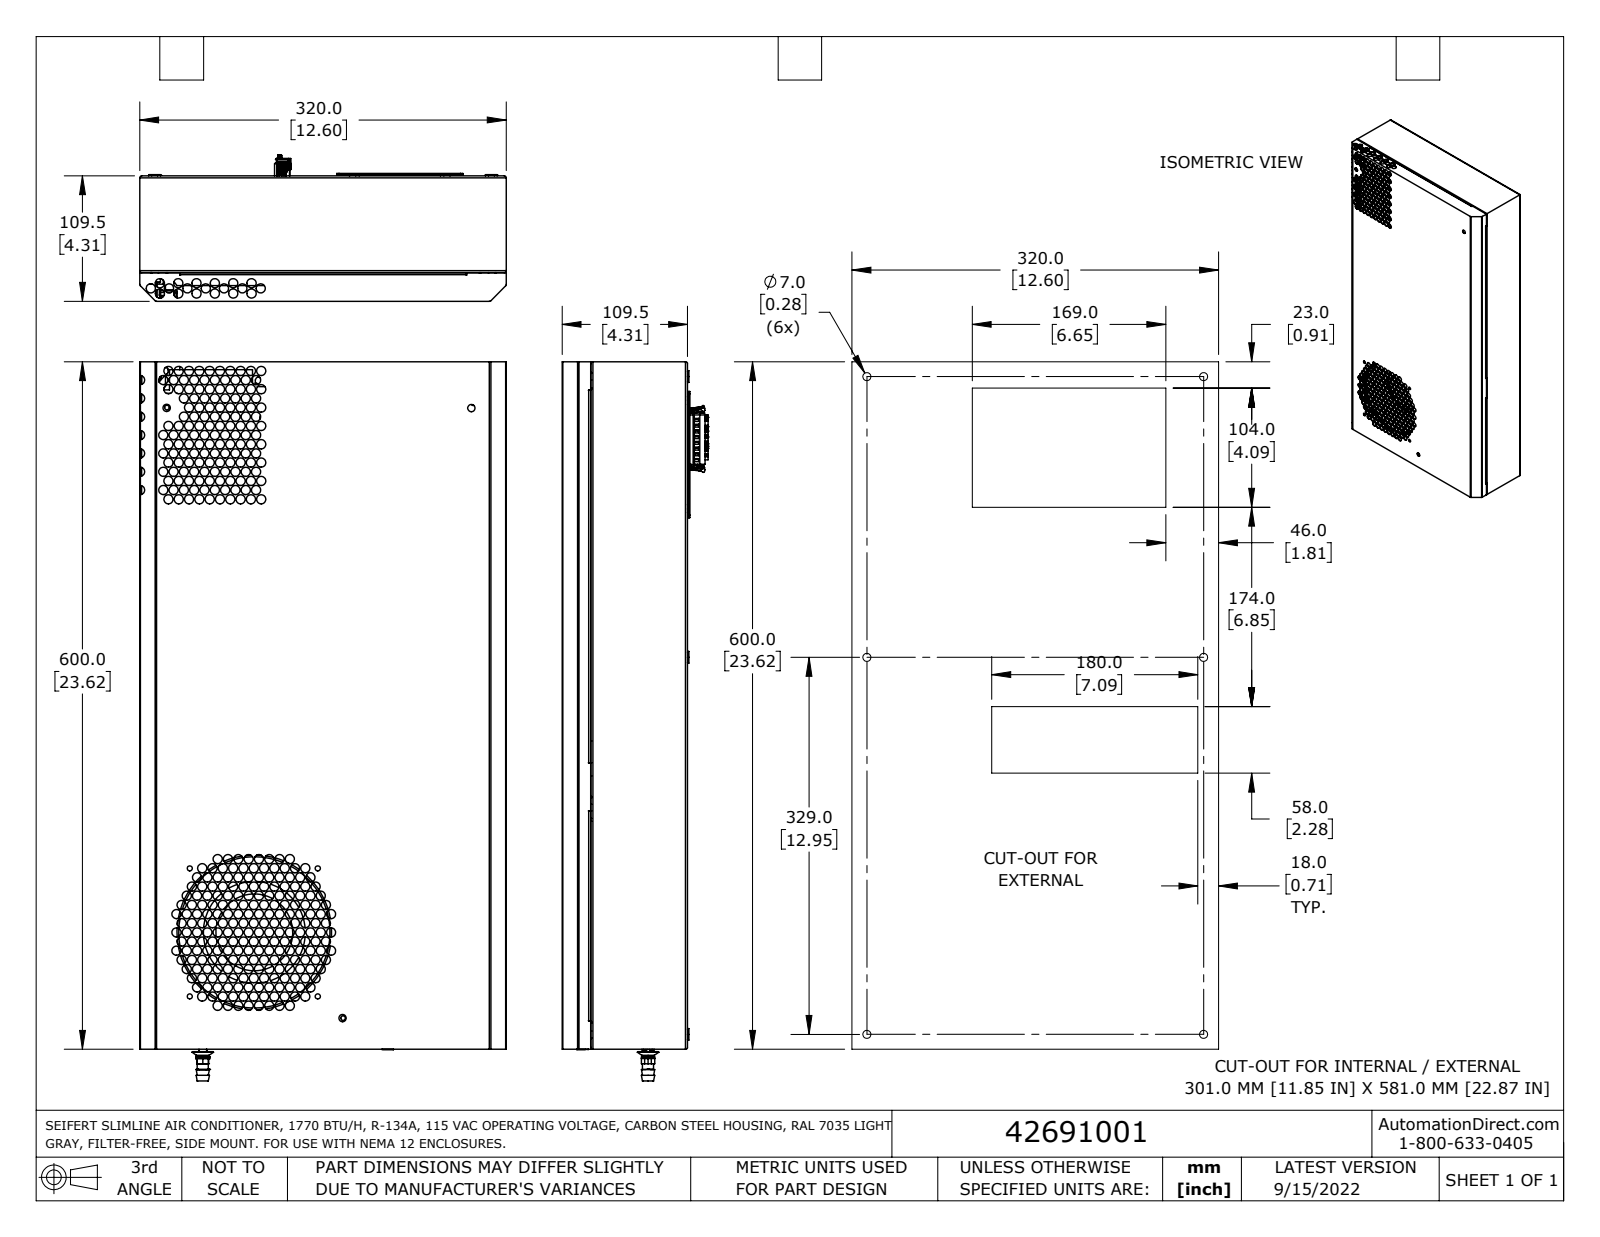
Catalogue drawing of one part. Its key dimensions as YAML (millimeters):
part_name: "42691001"
step_written_by: "SolidWorks 2021 (AUTOMOTIVE_DESIGN)"
units: millimeters
bodies: {solids: 3, faces: 1330, planar: 1083, cylindrical: 206, other: 41}
overall_size: [600, 320, 127.5]
volume: 465400
surface_area: 1146000
round_holes:
  - {diameter: 1.8, count: 8}
  - {diameter: 3.6, count: 8}
  - {diameter: 4.2, count: 7}
  - {diameter: 4.3, count: 3}
  - {diameter: 6.5, count: 2}
  - {diameter: 10.5, count: 1}
partial_cylinders:
  - {radius: 4, count: 23}
  - {radius: 1.8, count: 19}
  - {radius: 0.8, count: 12}
  - {radius: 1, count: 10}
  - {radius: 2.9, count: 8}
  - {radius: 1.5, count: 6}
  - {radius: 0.3, count: 4}
  - {radius: 0.4, count: 4}
face_to_face_distances: [0.8, 108.7, 109.5, 107.9, 319.2, 599.2, 318.4, 320, 83.7, 25]
hole_center_spacings: [5, 10, 15, 0.9, 20, 4.8, 5.4, 9.7]
